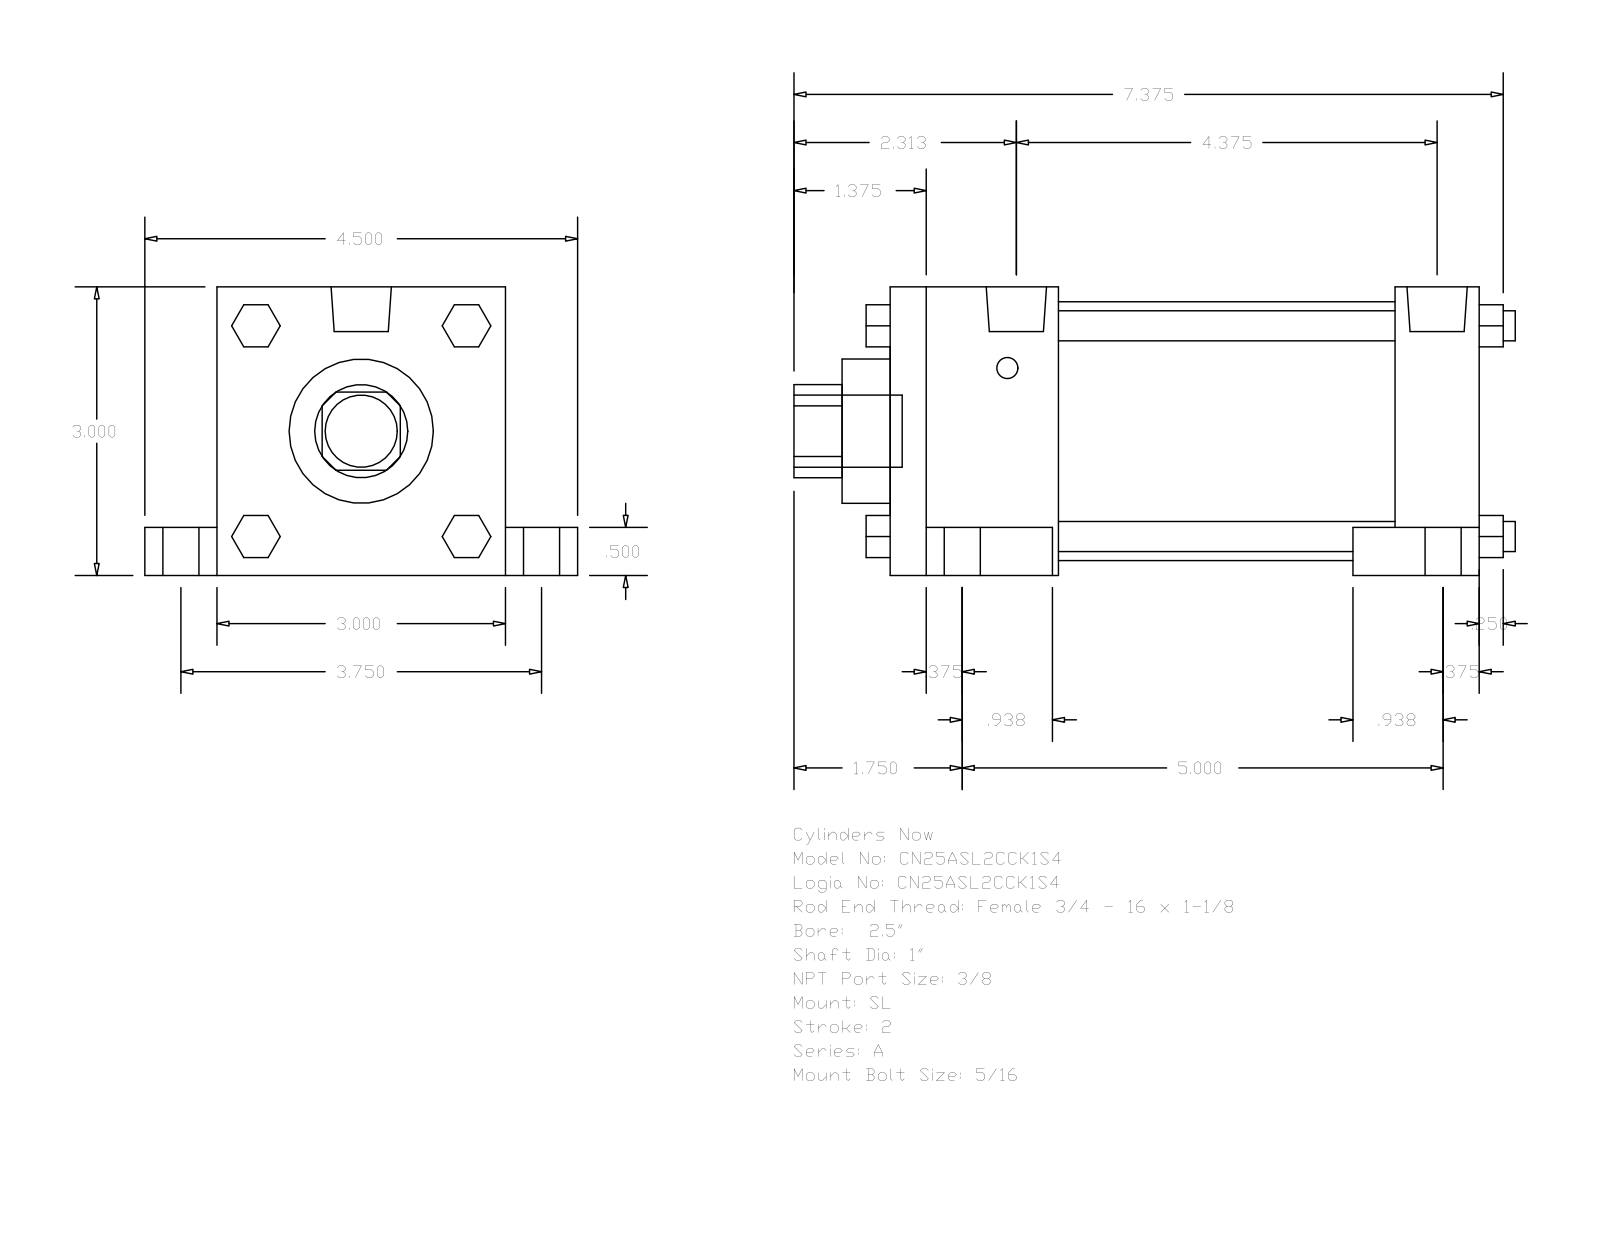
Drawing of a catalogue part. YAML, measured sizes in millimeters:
part_name: "A_SL__0250_1"
step_written_by: "GSSL Pune (CONFIG_CONTROL_DESIGN)"
units: millimeters
bodies: {solids: 0, faces: 148, planar: 112, cylindrical: 36, other: 0}
overall_size: [190.5, 114.3, 76.2]
round_holes:
  - {diameter: 25.4, count: 1}
  - {diameter: 38.1, count: 1}
  - {diameter: 68.33, count: 1}
round_bosses_or_shafts:
  - {diameter: 15.88, count: 4}
  - {diameter: 9.53, count: 4}
  - {diameter: 7.94, count: 4}
  - {diameter: 5.56, count: 4}
  - {diameter: 15.93, count: 2}
  - {diameter: 19.05, count: 1}
partial_cylinders:
  - {radius: 12.29, count: 1}
face_to_face_distances: [76.2, 155.57, 12.7, 22.22, 44.45, 111.12, 133.35, 88.9, 19.05, 63.5]
